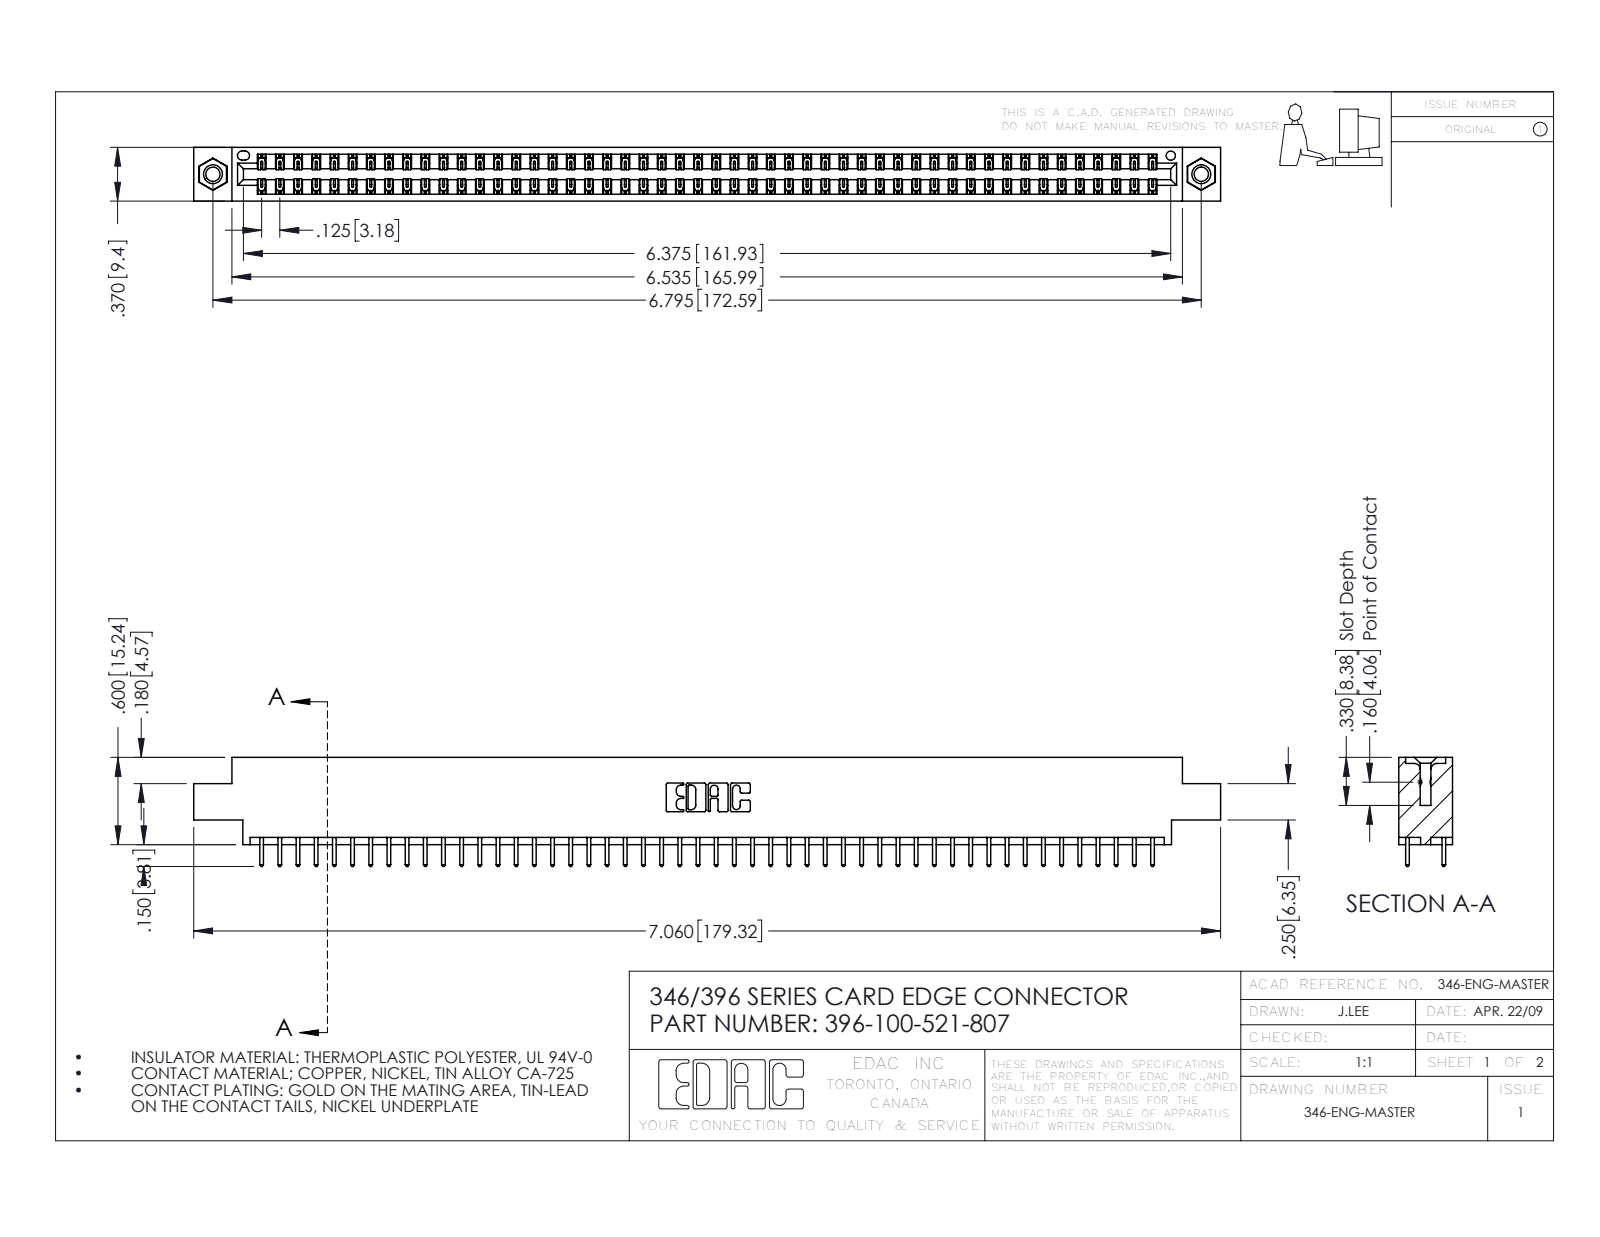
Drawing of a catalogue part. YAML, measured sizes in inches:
part_name: "345-250-001_345-250-005-103; 346 Part_0.170 Offset - 0.156 Dia-TI; 345-292-001_345-293-121; 396-100-521-807"
step_written_by: "SolidWorks 2016 (CONFIG_CONTROL_DESIGN)"
units: inches
bodies: {solids: 103, faces: 5386, planar: 3612, cylindrical: 1758, other: 16}
overall_size: [7.06, 0.75, 0.37]
volume: 1.058
surface_area: 37.04
round_holes:
  - {diameter: 0.098, count: 2}
  - {diameter: 0.125, count: 2}
  - {diameter: 0.156, count: 2}
  - {diameter: 0.064, count: 1}
round_bosses_or_shafts:
  - {diameter: 0.155, count: 2}
partial_cylinders:
  - {radius: 0.006, count: 150}
  - {radius: 0.01, count: 100}
  - {radius: 0.01, count: 22}
  - {radius: 0.007, count: 6}
  - {radius: 0.031, count: 6}
  - {radius: 0.026, count: 3}
  - {radius: 0.014, count: 2}
  - {radius: 0.022, count: 2}
face_to_face_distances: [0.048, 0.322, 0.37, 0.25, 0.072, 0.298, 0.025, 0.275, 0.222, 0.148]
hole_center_spacings: [0.246, 6.586, 6.795]
